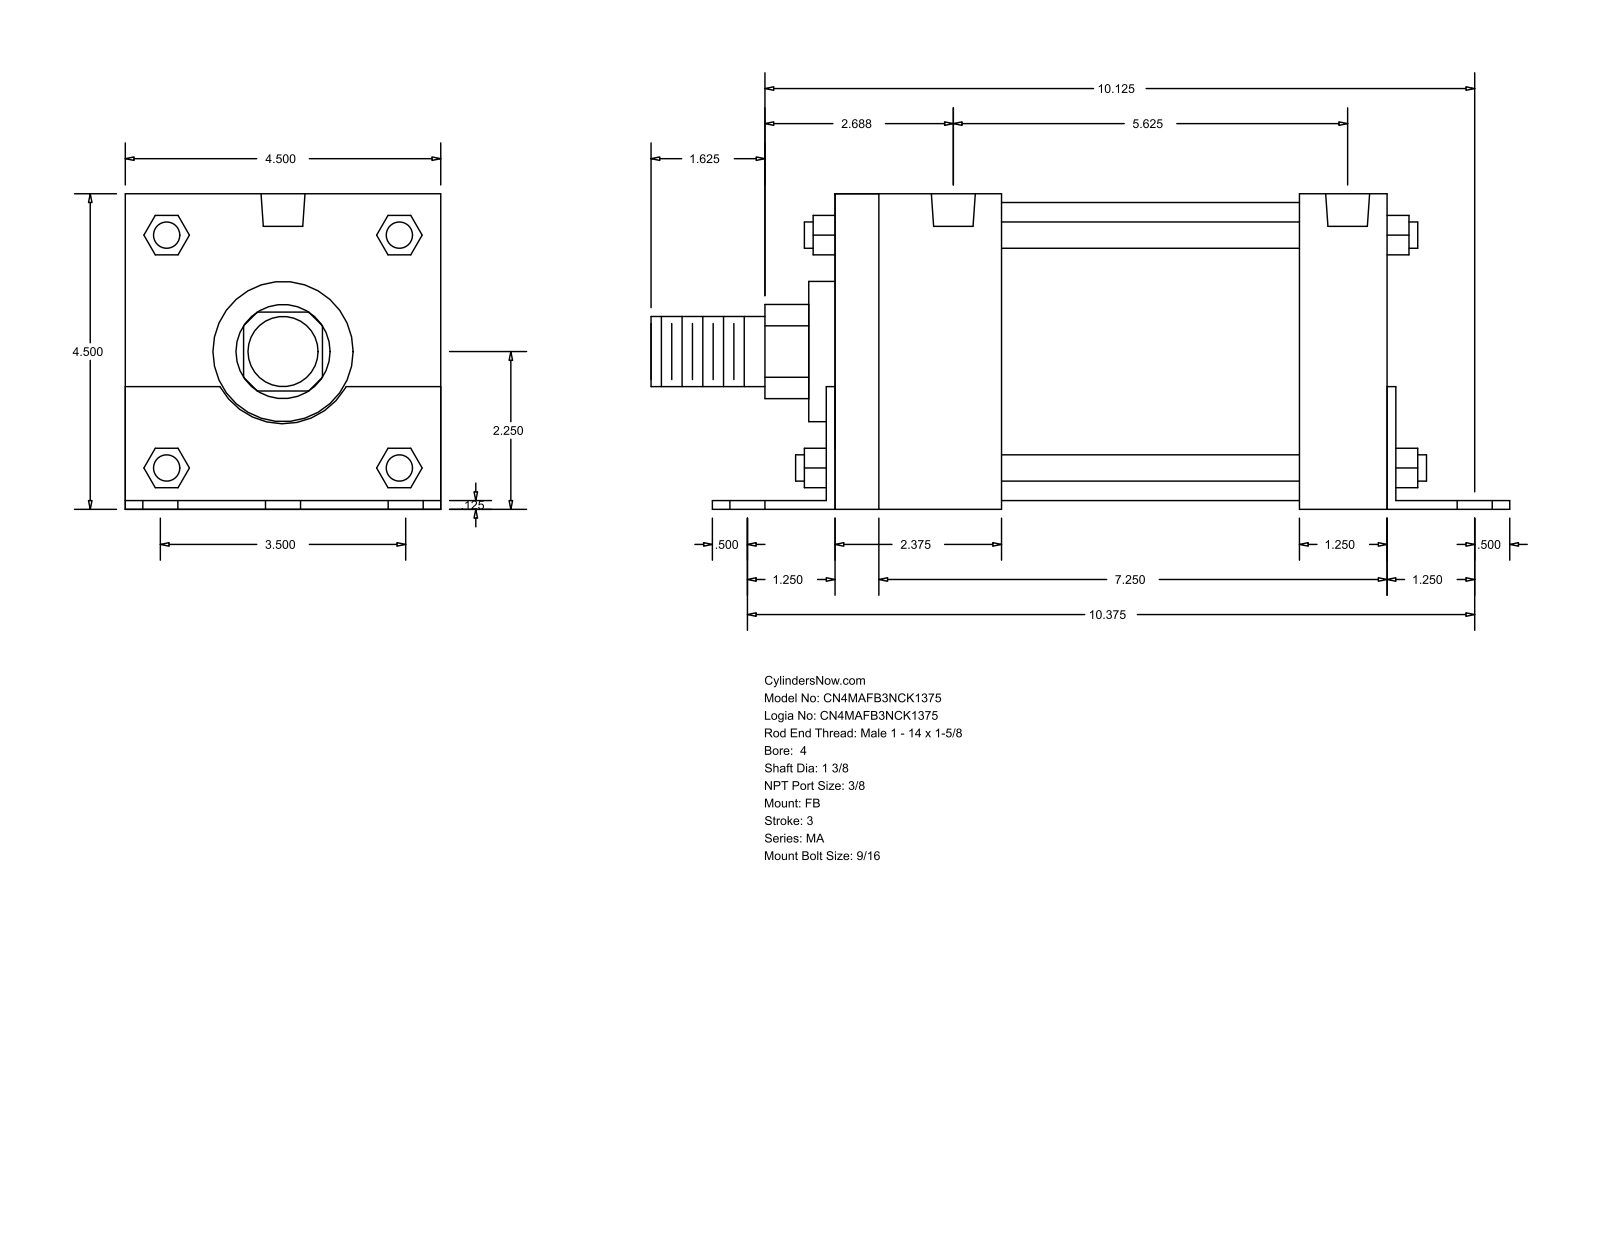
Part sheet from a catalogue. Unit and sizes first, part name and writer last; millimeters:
Units: millimetres
Overall size (bounding box): 311.15 × 114.35 × 114.3
Round holes (diameter × count): ⌀14.29 ×6, ⌀11.11 ×4, ⌀15.93 ×2
Round bosses / shafts (diameter × count): ⌀9.53 ×4, ⌀107.95 ×1, ⌀50.8 ×1, ⌀34.92 ×1, ⌀25.4 ×1
Partial cylindrical surfaces — rounded edges, fillets, slot ends (radius × count): R17.06 ×1, R26.16 ×1
Main face-to-face distances: 114.3, 3.17, 114.35, 3.12, 111.18, 203.2, 200.03, 206.37, 31.75, 171.45
Hole centre spacings: 44.45, 267.25, 263.53, 64, 67.5, 86.85, 88.9, 90.98
Bodies: 0 solids, 140 faces (105 planar, 35 cylindrical, 0 other)
Part name (STEP PRODUCT): MA_FB__0400_1.375
STEP written by: GSSL Pune (CONFIG_CONTROL_DESIGN)
